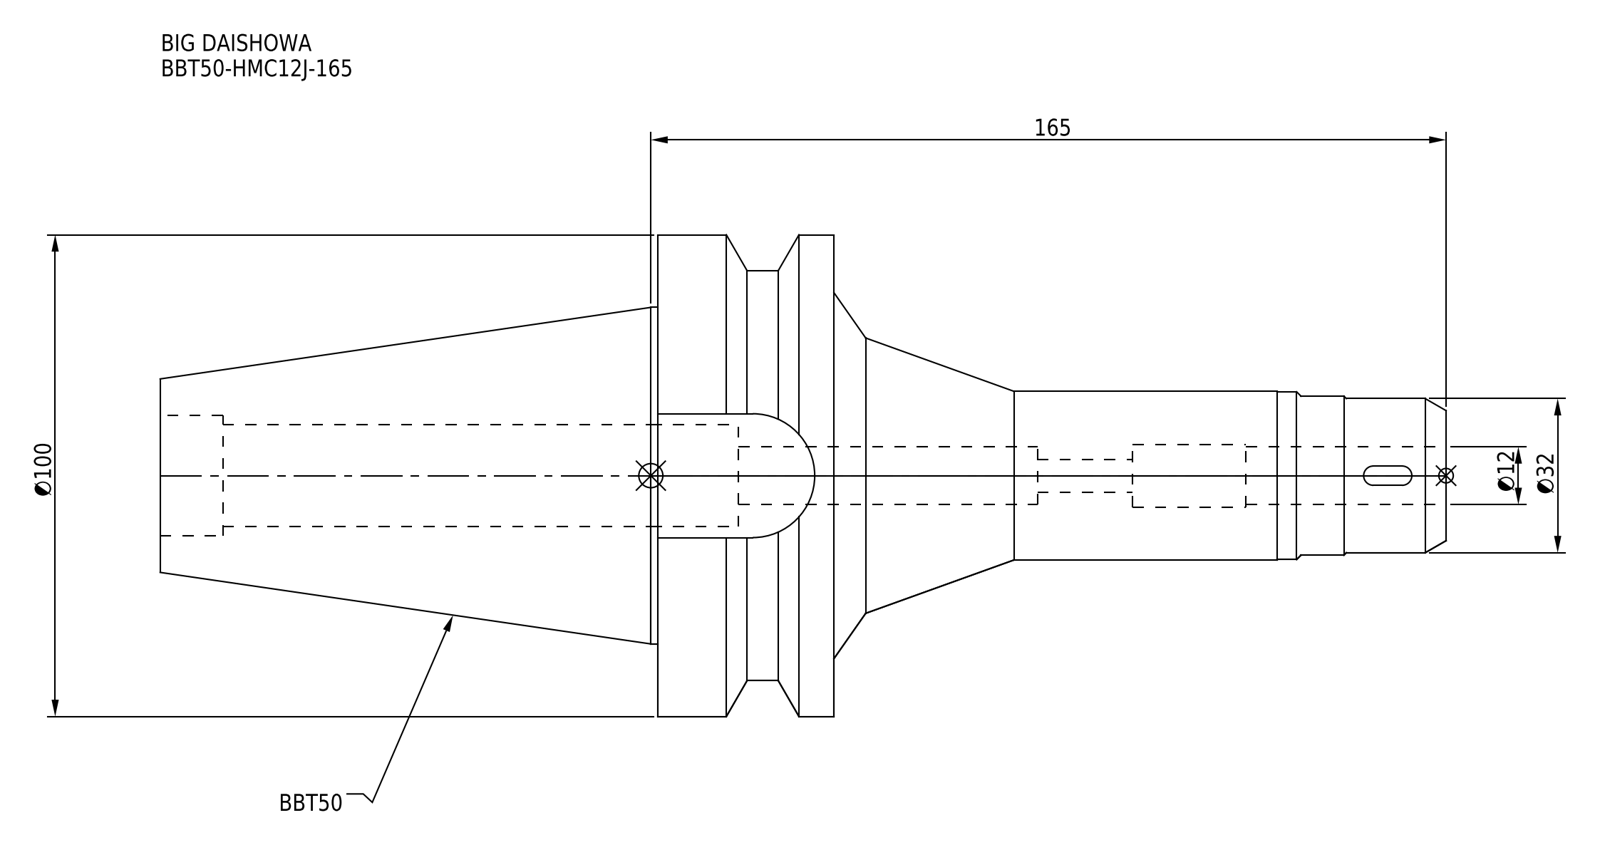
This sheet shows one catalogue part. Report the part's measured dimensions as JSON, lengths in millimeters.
{"part_name": "BBT50-HMC12J-165", "step_written_by": "CREO PARAMETRIC BY PTC INC, 2016380 (AUTOMOTIVE_DESIGN)", "units": "millimeters", "bodies": {"solids": 1, "faces": 88, "planar": 32, "cylindrical": 40, "other": 16}, "overall_size": [266.8, 100, 100], "volume_mm3": 595742, "surface_area_mm2": 72065, "round_holes": [[6.8, 1], [12, 1], [13, 1], [21.2, 1], [25, 1]], "round_bosses_or_shafts": [[100, 1], [85, 1], [69.85, 1], [35, 1], [34.8, 1], [33, 1], [32, 1]], "partial_cylinders_radius": [[2, 4], [12.85, 1]], "face_to_face_distances": [36.5, 139.8, 103.3, 70.8, 127, 163.5, 266.8, 25.7, 19.8, 146.8]}
